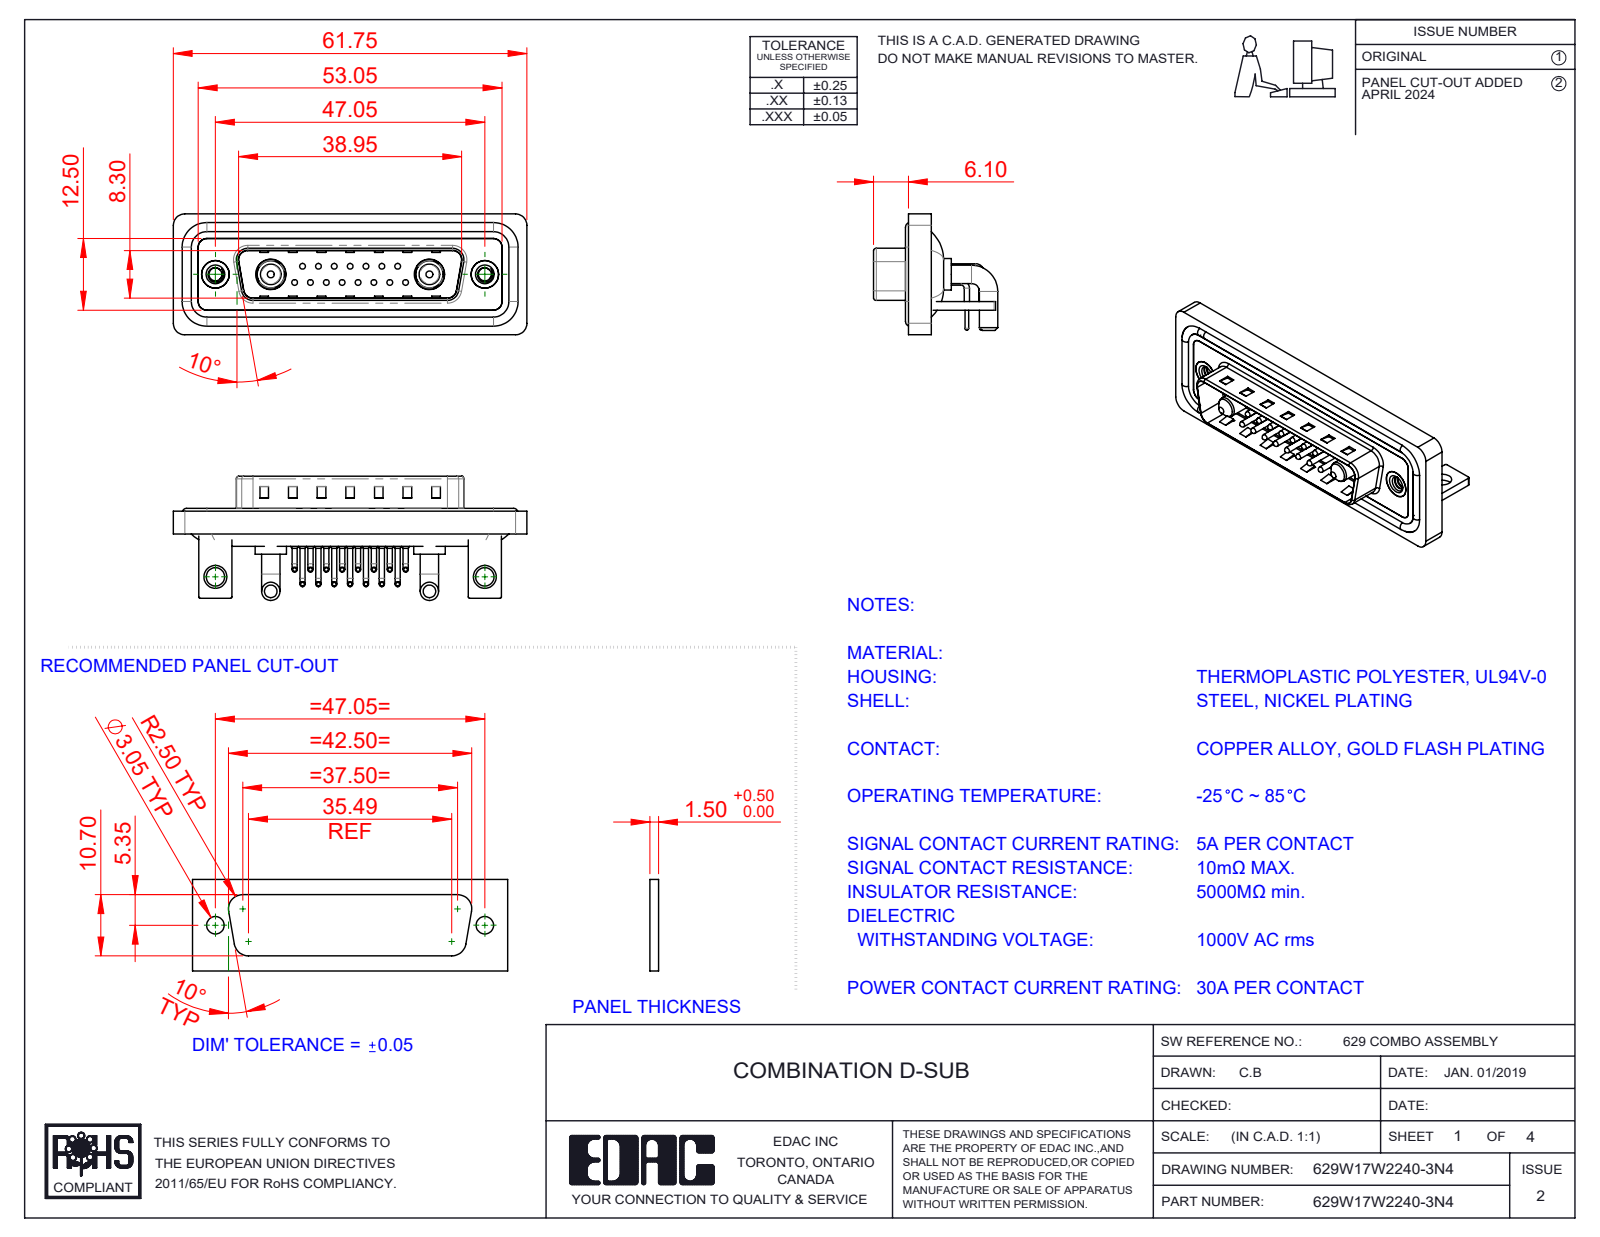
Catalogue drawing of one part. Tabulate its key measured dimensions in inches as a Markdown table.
| quantity | value |
| --- | --- |
| part name | 629Combo Shell Rear_25 Contacts; 629Combo Housing_17W2; 629Combo Contact Row 2; 629Combo Stabilizer Bracket (+6 more) |
| STEP written by | SolidWorks 2023 (CONFIG_CONTROL_DESIGN) |
| units | inches |
| bodies | 28 solids, 2259 faces (1209 planar, 788 cylindrical, 262 other) |
| overall size | 2.431 × 0.854 × 0.831 |
| volume | 0.479 in³ |
| surface area | 20.5 in² |
| round holes (diameter × count) | 0.03 × 15, 0.063 × 15, 0.079 × 15, 0.089 × 2, 0.126 × 2, 0.157 × 2, 0.189 × 2, 0.191 × 2, 0.197 × 2, 0.209 × 2 |
| round bosses / shafts (diameter × count) | 0.035 × 30, 0.059 × 15, 0.039 × 15, 0.026 × 15, 0.126 × 4, 0.063 × 4, 0.217 × 2, 0.205 × 2 |
| partial cylindrical surfaces (radius × count) | 0.079 × 19, 0.059 × 18, 0.01 × 16, 0.04 × 15, 0.02 × 9, 0.063 × 8, 0.024 × 4, 0.026 × 4 |
| main face-to-face distances | 0.016, 0.031, 0.059, 0.083, 0.114, 0.043, 0.161, 0.063, 0.177, 0.146 |
| hole center spacings | 0.124, 0.109, 0.218, 0.327, 0.198, 0.295, 0.436, 0.198 |
